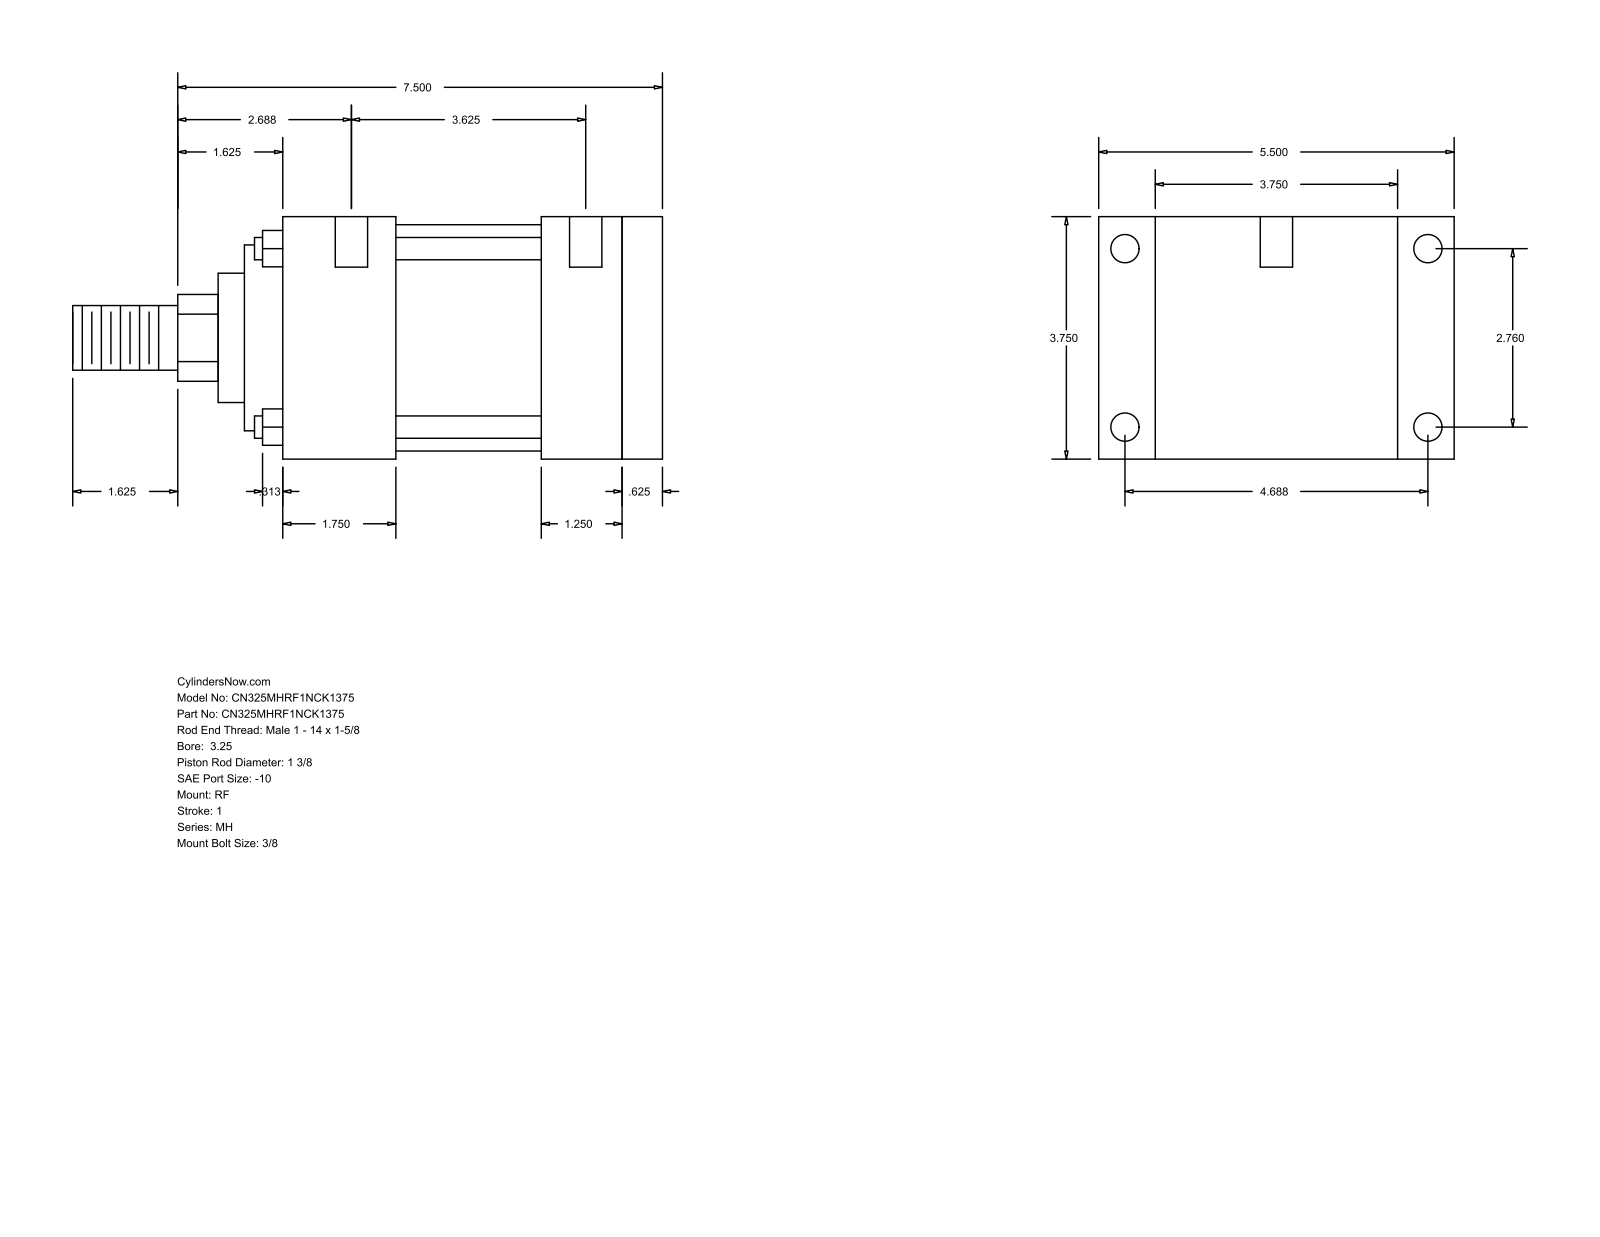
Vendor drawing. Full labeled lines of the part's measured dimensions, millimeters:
Part name (STEP PRODUCT): MH_RF__0325_1.375
STEP written by: GSSL Pune (CONFIG_CONTROL_DESIGN)
Units: millimetres
Bodies: 0 solids, 94 faces (65 planar, 29 cylindrical, 0 other)
Overall size (bounding box): 231.78 × 139.7 × 95.25
Round holes (diameter × count): ⌀5.56 ×4, ⌀11.13 ×4, ⌀12.7 ×2
Round bosses / shafts (diameter × count): ⌀8.76 ×4, ⌀88.9 ×1, ⌀73.03 ×1, ⌀50.8 ×1, ⌀34.92 ×1, ⌀25.4 ×1
Partial cylindrical surfaces — rounded edges, fillets, slot ends (radius × count): R17.06 ×1
Main face-to-face distances: 95.24, 149.23, 15.88, 133.35, 22.23, 117.47, 44.45, 88.9, 104.78, 101.61
Hole centre spacings: 70.1, 98.43, 119.06, 138.16, 1.59, 4.76, 92.08, 93.67
